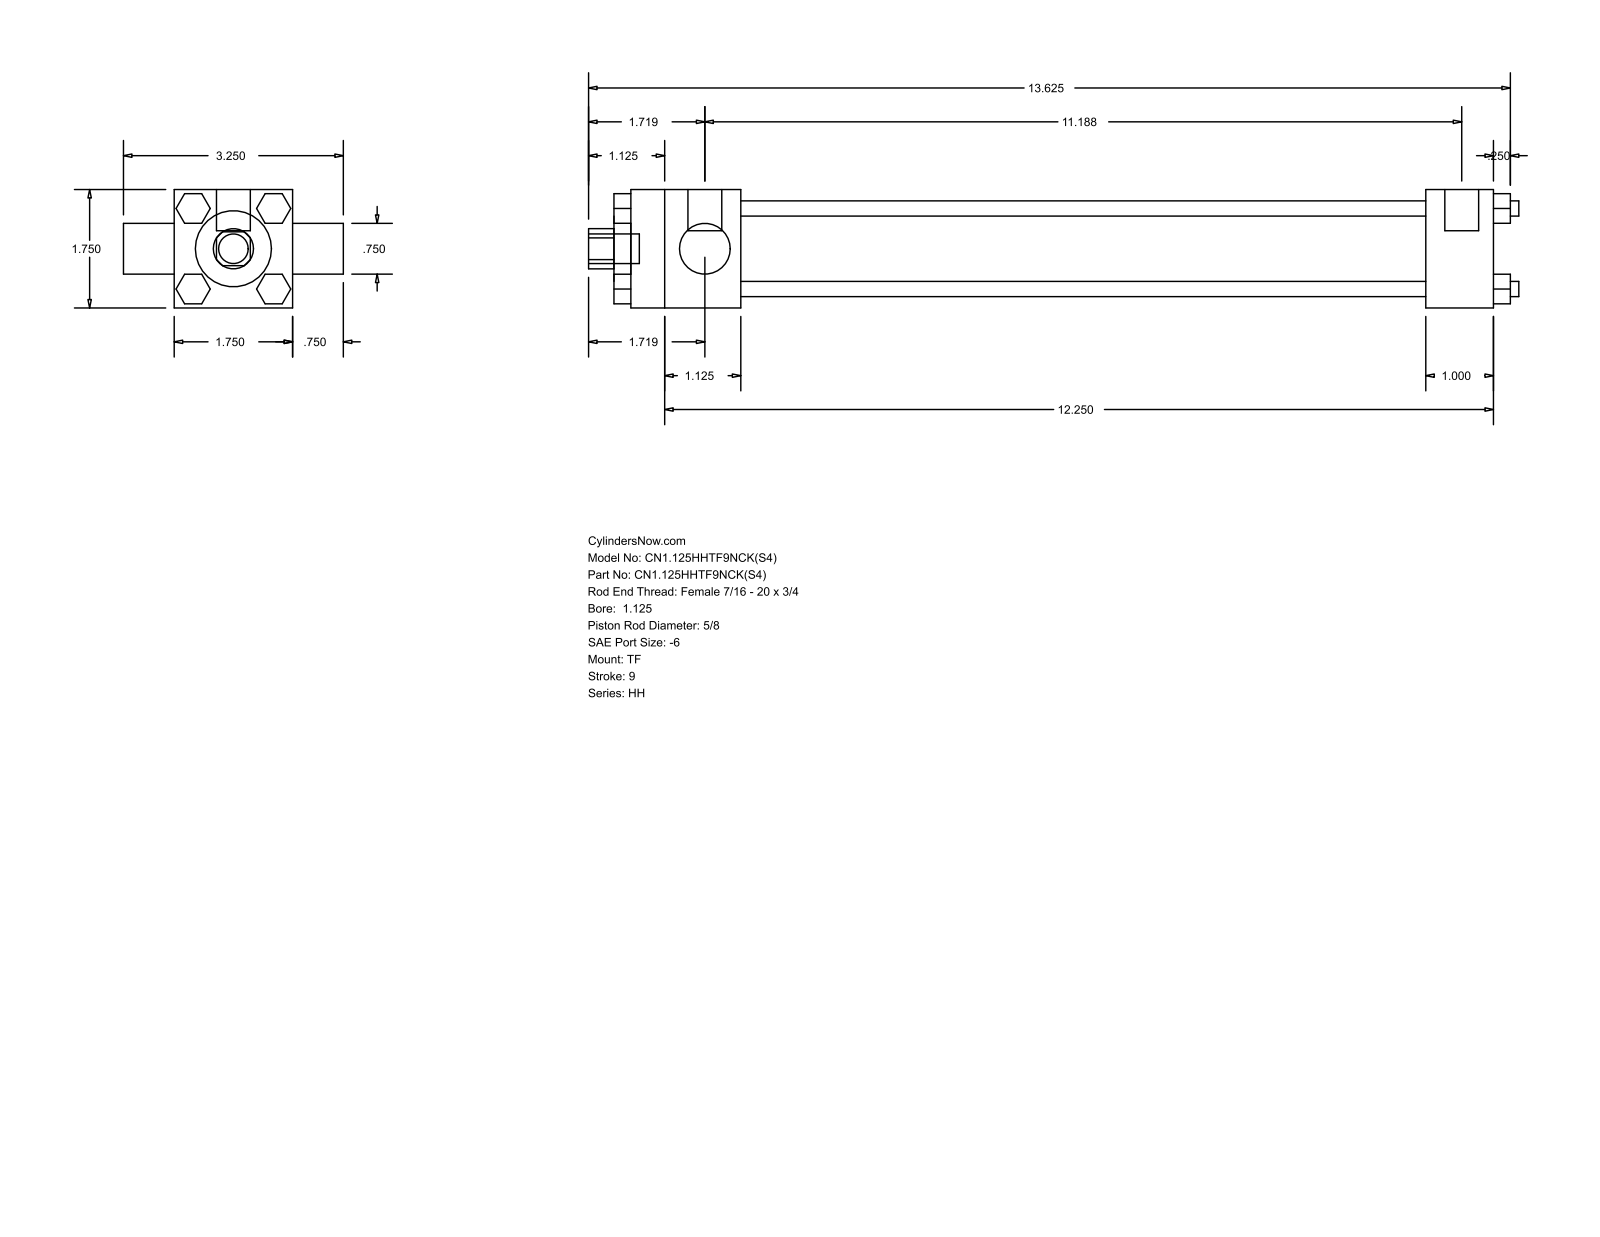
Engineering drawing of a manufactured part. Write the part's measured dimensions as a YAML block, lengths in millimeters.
part_name: "HH_TF__0112_0.625"
step_written_by: "GSSL Pune (CONFIG_CONTROL_DESIGN)"
units: millimeters
bodies: {solids: 0, faces: 120, planar: 92, cylindrical: 28, other: 0}
overall_size: [349.25, 82.55, 44.45]
round_holes:
  - {diameter: 15.88, count: 1}
  - {diameter: 19.05, count: 1}
  - {diameter: 28.57, count: 1}
  - {diameter: 34.92, count: 1}
round_bosses_or_shafts:
  - {diameter: 5.71, count: 4}
  - {diameter: 5.56, count: 3}
  - {diameter: 12.7, count: 2}
  - {diameter: 11.11, count: 1}
partial_cylinders:
  - {radius: 7.54, count: 1}
face_to_face_distances: [44.46, 11.11, 257.17, 282.58, 25.41, 41.27, 298.44, 323.85, 47.62, 330.2]
